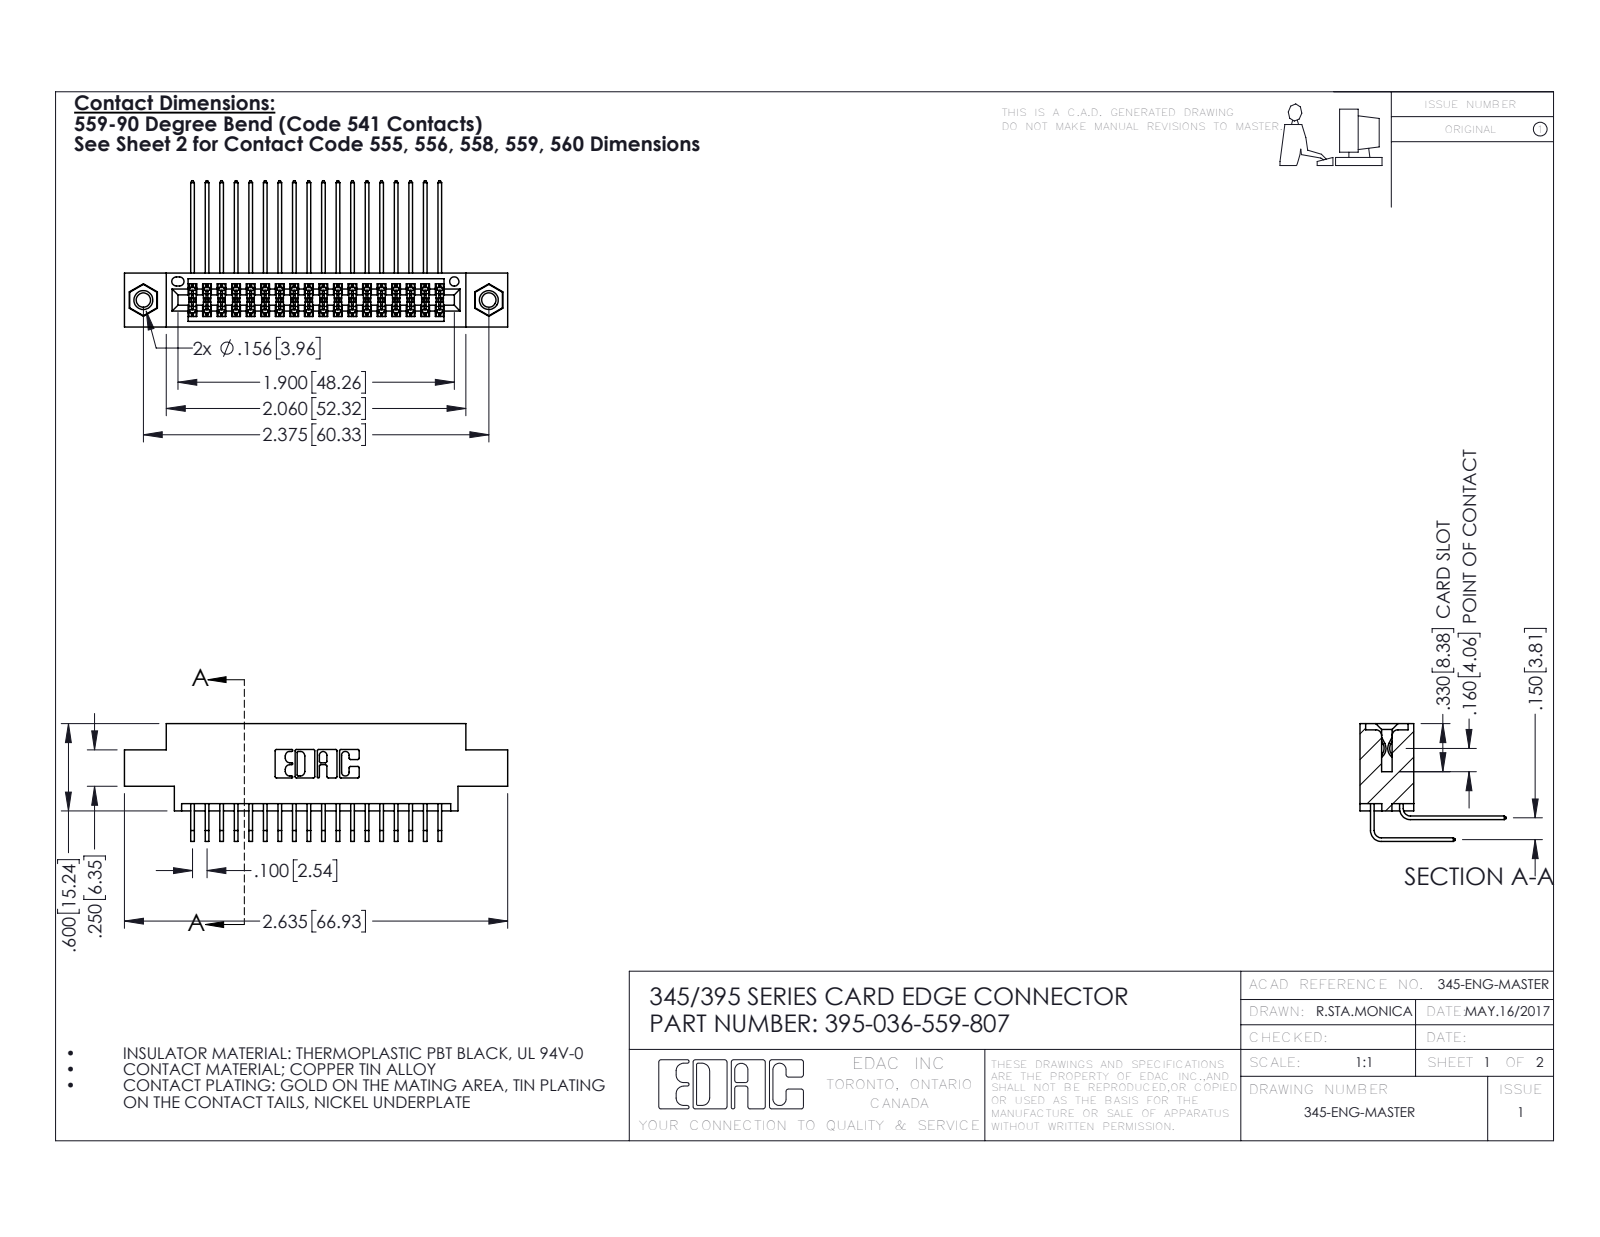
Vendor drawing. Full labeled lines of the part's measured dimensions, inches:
Part name (STEP PRODUCT): 345 Part_0.170 Offset - 0.156 Dia-TI; 345-292-001_558 559 Tail - 1; 395-036-559-807; 345-292-001_559 Tail - 2 (+1 more)
STEP written by: SolidWorks 2016 (CONFIG_CONTROL_DESIGN)
Units: inches
Bodies: 39 solids, 2062 faces (1376 planar, 670 cylindrical, 16 other)
Overall size (bounding box): 2.635 × 1.005 × 0.809
Volume: 0.388 in³ · Surface area: 15.63 in²
Round holes (diameter × count): ⌀0.098 ×2, ⌀0.125 ×2, ⌀0.156 ×2, ⌀0.064 ×1
Round bosses / shafts (diameter × count): ⌀0.155 ×2
Partial cylindrical surfaces — rounded edges, fillets, slot ends (radius × count): R0.006 ×54, R0.01 ×22, R0.007 ×6, R0.031 ×6, R0.026 ×3, R0.014 ×2, R0.019 ×2, R0.022 ×2
Main face-to-face distances: 0.072, 0.298, 0.37, 0.2, 0.098, 0.272, 0.025, 0.15, 0.225, 0.175
Hole centre spacings: 0.27, 2.141, 2.375
